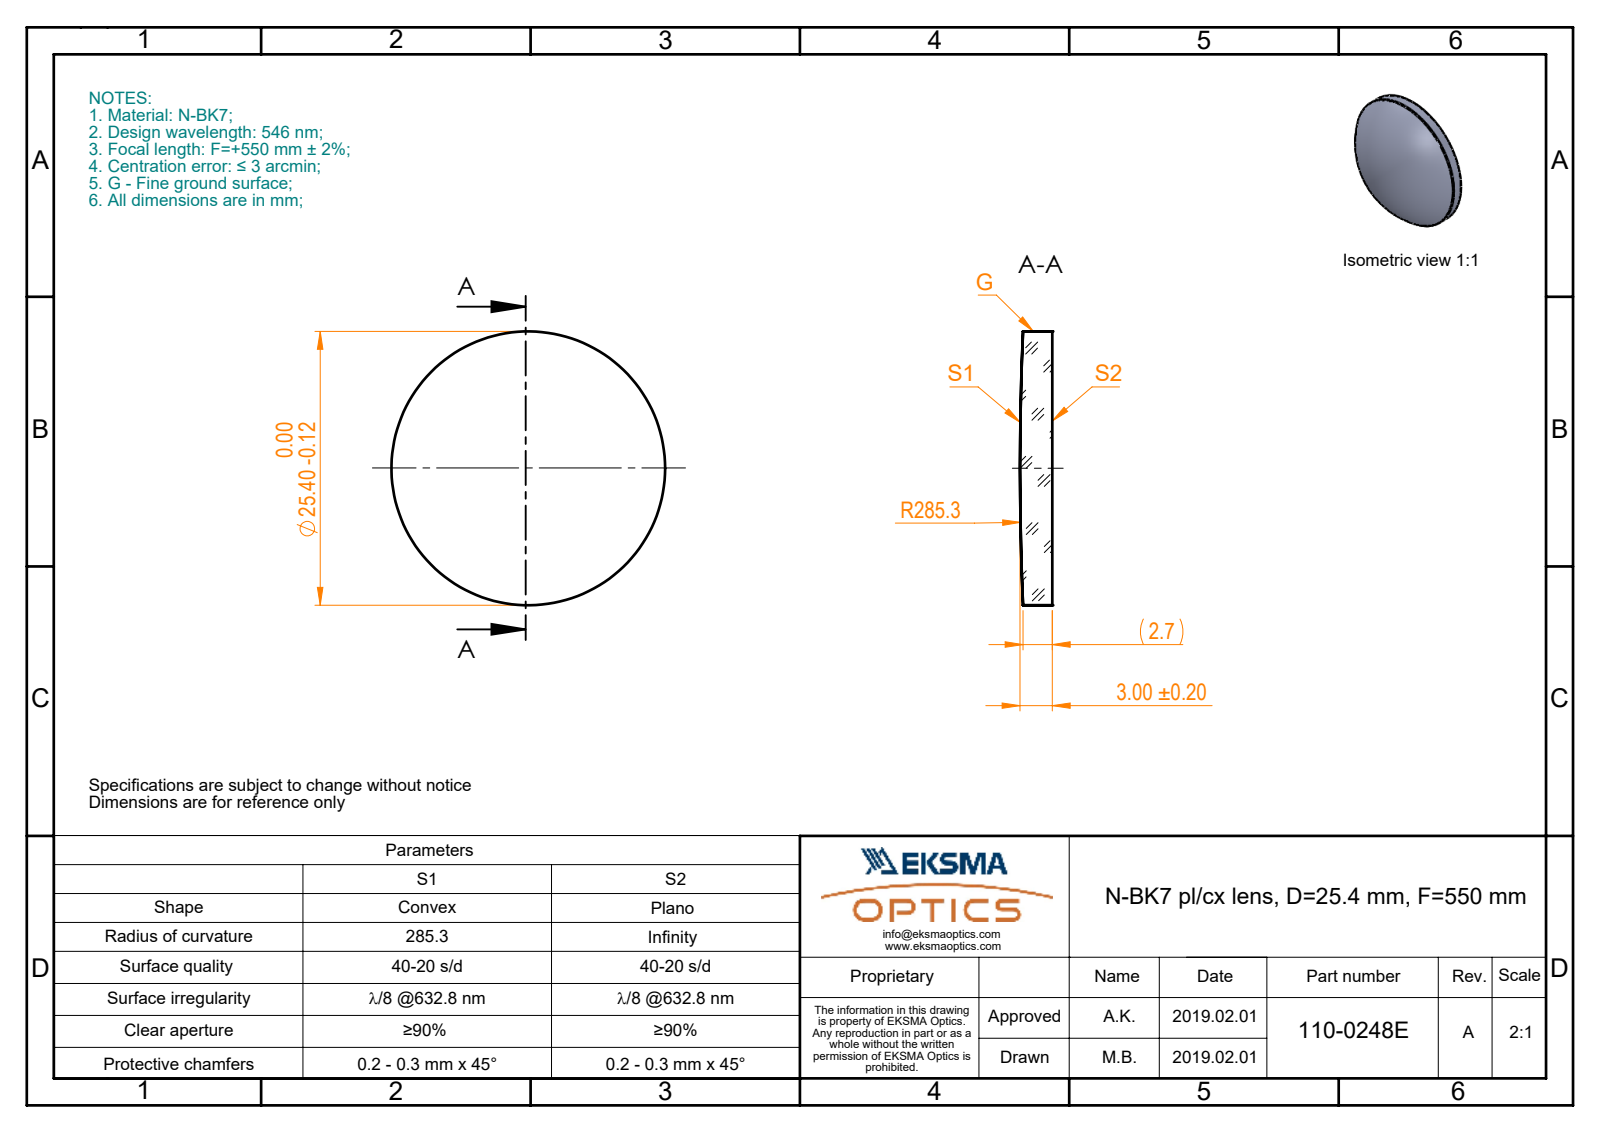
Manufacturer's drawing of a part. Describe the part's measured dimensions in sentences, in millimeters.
The part is named "110-0248E BK7 pl-cx 25.4 F550". Its 3-D file was written by "SolidWorks 2017 (CONFIG_CONTROL_DESIGN)". It is 1 solid with 5 faces: 1 planar, 2 cylindrical and 2 other. Overall it measures 25.4 by 25.4 by 3 millimeters. Its volume is 1 448 cubic millimeters and its surface area 1 230 square millimeters. Round bosses or shafts: 1 of diameter 25.4.
